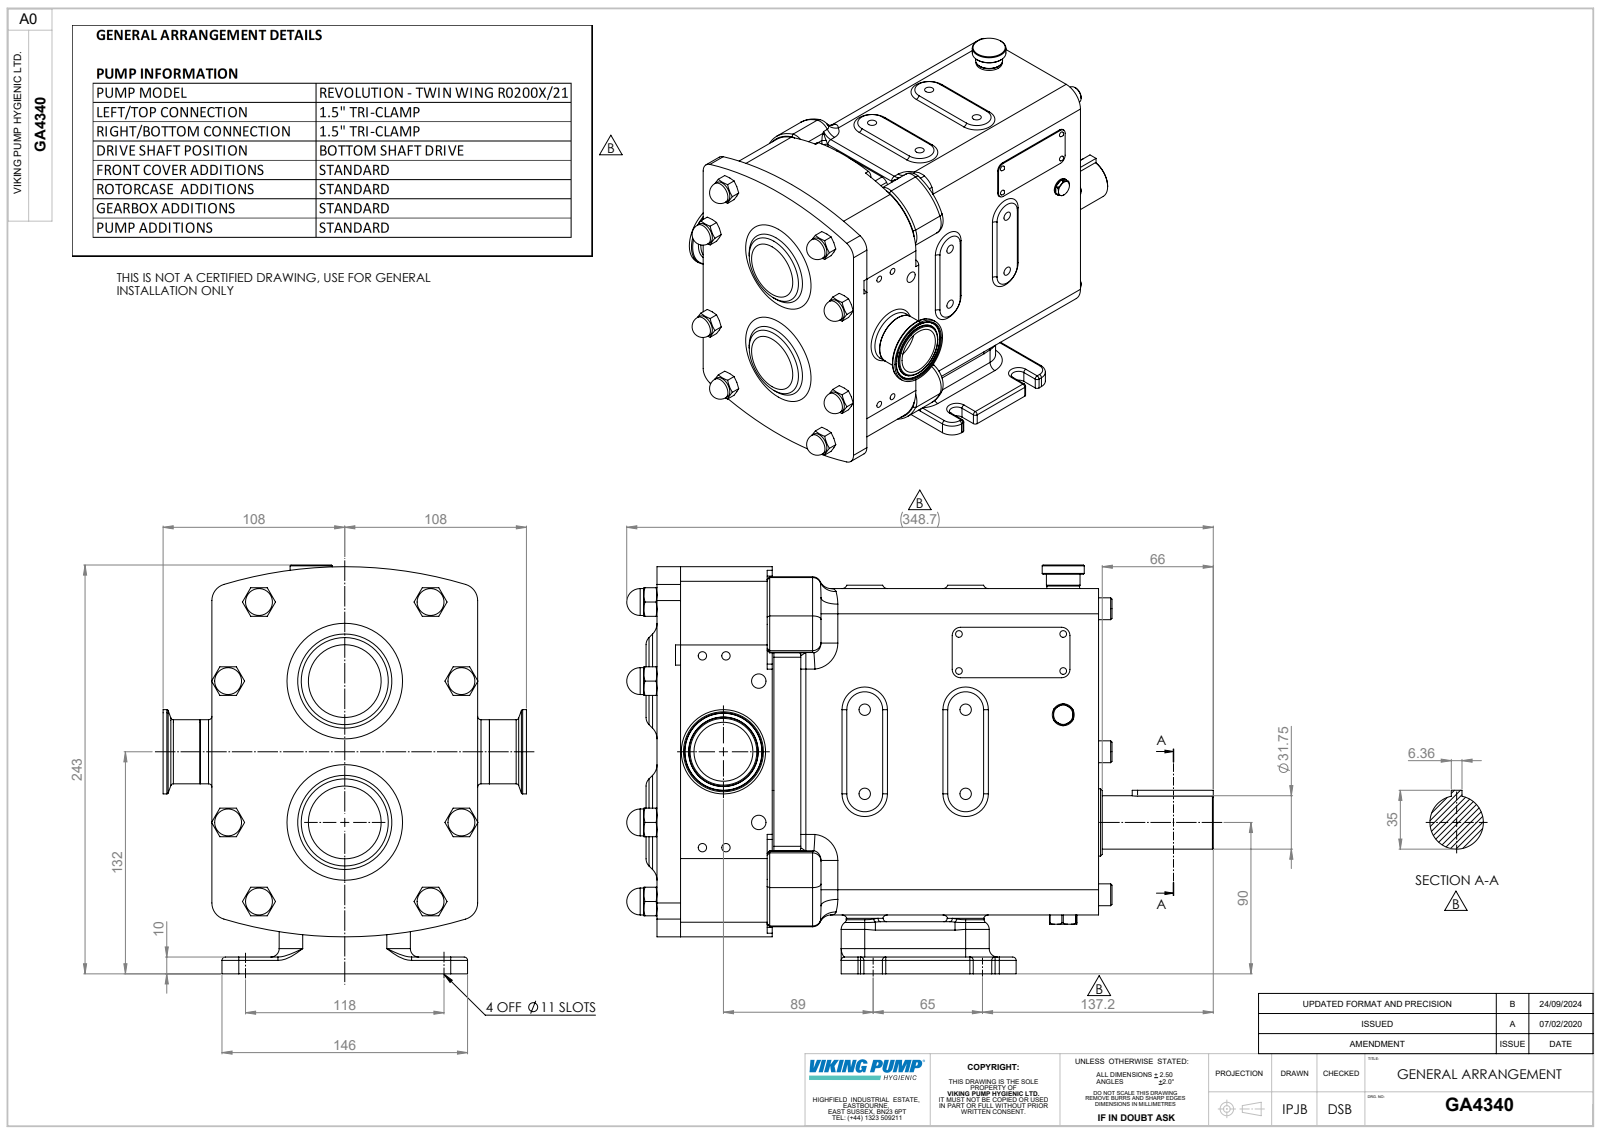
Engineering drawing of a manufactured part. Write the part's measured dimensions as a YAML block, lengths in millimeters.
part_name: "Copy of R0200 RLP H BSD^GA4340; Copy of RA94-5121-22M^GA4340; GA4340"
step_written_by: "SolidWorks 2023 (AUTOMOTIVE_DESIGN)"
units: millimeters
bodies: {solids: 3, faces: 1007, planar: 316, cylindrical: 320, other: 371}
overall_size: [348.7, 243, 216]
volume: 6642000
surface_area: 373099
round_holes:
  - {diameter: 6.8, count: 8}
  - {diameter: 11, count: 8}
  - {diameter: 5, count: 4}
  - {diameter: 8.6, count: 2}
  - {diameter: 44, count: 2}
  - {diameter: 23, count: 1}
  - {diameter: 35.05, count: 1}
round_bosses_or_shafts:
  - {diameter: 16, count: 8}
  - {diameter: 13, count: 7}
  - {diameter: 50.1, count: 1}
  - {diameter: 40, count: 1}
  - {diameter: 38.1, count: 1}
  - {diameter: 38, count: 1}
  - {diameter: 31.75, count: 1}
  - {diameter: 25, count: 1}
partial_cylinders:
  - {radius: 10, count: 30}
  - {radius: 3, count: 28}
  - {radius: 2, count: 24}
  - {radius: 5, count: 19}
  - {radius: 5.9, count: 8}
  - {radius: 15, count: 8}
  - {radius: 5.5, count: 4}
  - {radius: 8, count: 4}
face_to_face_distances: [194, 68.5, 24, 110, 262.5, 193, 1, 69.5, 134, 22]
hole_center_spacings: [69.35, 50, 50.46, 60, 78.1, 84, 108.93, 129.2]
